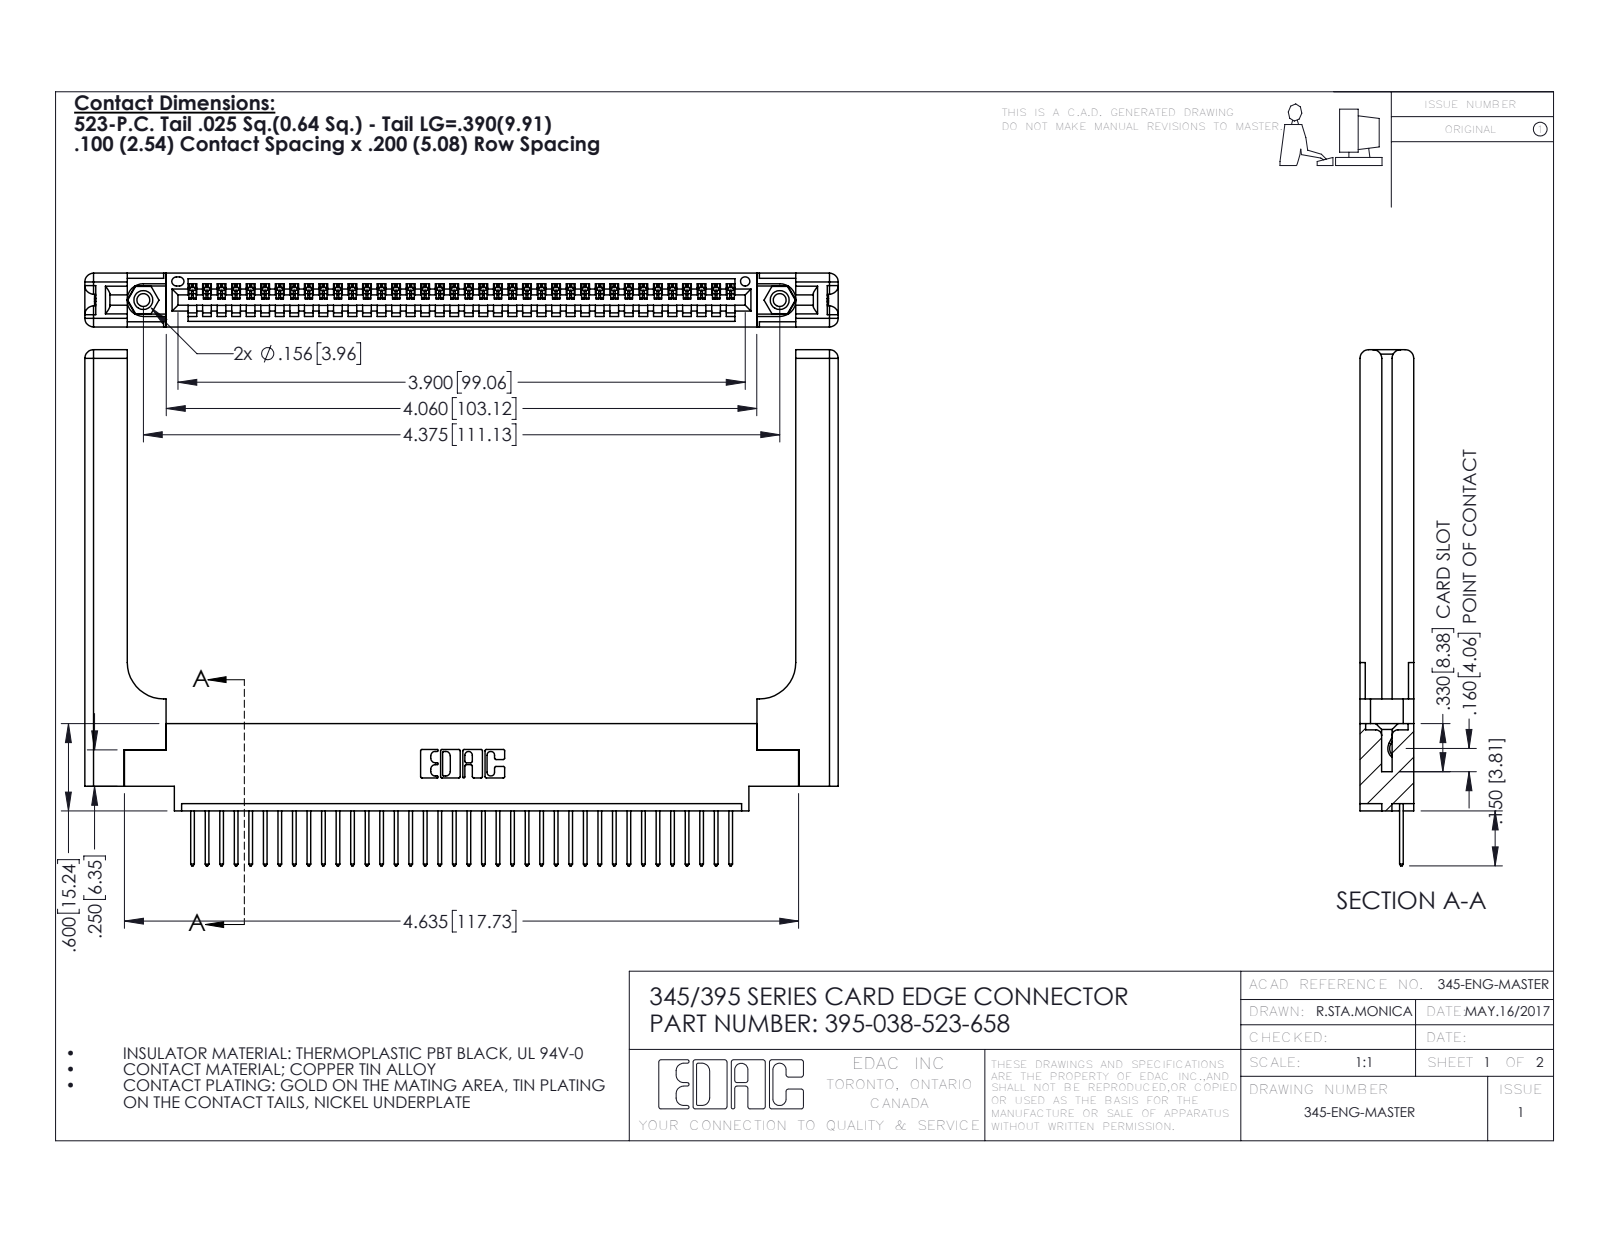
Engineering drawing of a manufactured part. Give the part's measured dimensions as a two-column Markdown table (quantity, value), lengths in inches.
| quantity | value |
| --- | --- |
| part name | 345-220-058_345-220-058; 345-292-001_345-293-123; 345 Part_0.170 Offset - 0.156 Dia-TH; 395-038-523-658 (+1 more) |
| STEP written by | SolidWorks 2016 (CONFIG_CONTROL_DESIGN) |
| units | inches |
| bodies | 43 solids, 2590 faces (1752 planar, 778 cylindrical, 60 other) |
| overall size | 5.179 × 3.547 × 0.37 |
| volume | 1.272 in³ |
| surface area | 33.8 in² |
| round holes (diameter × count) | 0.089 × 2, 0.125 × 2, 0.156 × 2, 0.064 × 1 |
| round bosses / shafts (diameter × count) | 0.155 × 2 |
| partial cylindrical surfaces (radius × count) | 0.006 × 76, 0.01 × 76, 0.01 × 22, 0.06 × 16, 0.007 × 6, 0.031 × 6, 0.026 × 3, 0.03 × 2 |
| main face-to-face distances | 0.37, 0.072, 0.298, 0.098, 0.272, 0.025, 0.2, 0.148, 0.15, 0.225 |
| hole center spacings | 0.27, 4.139, 4.375 |
